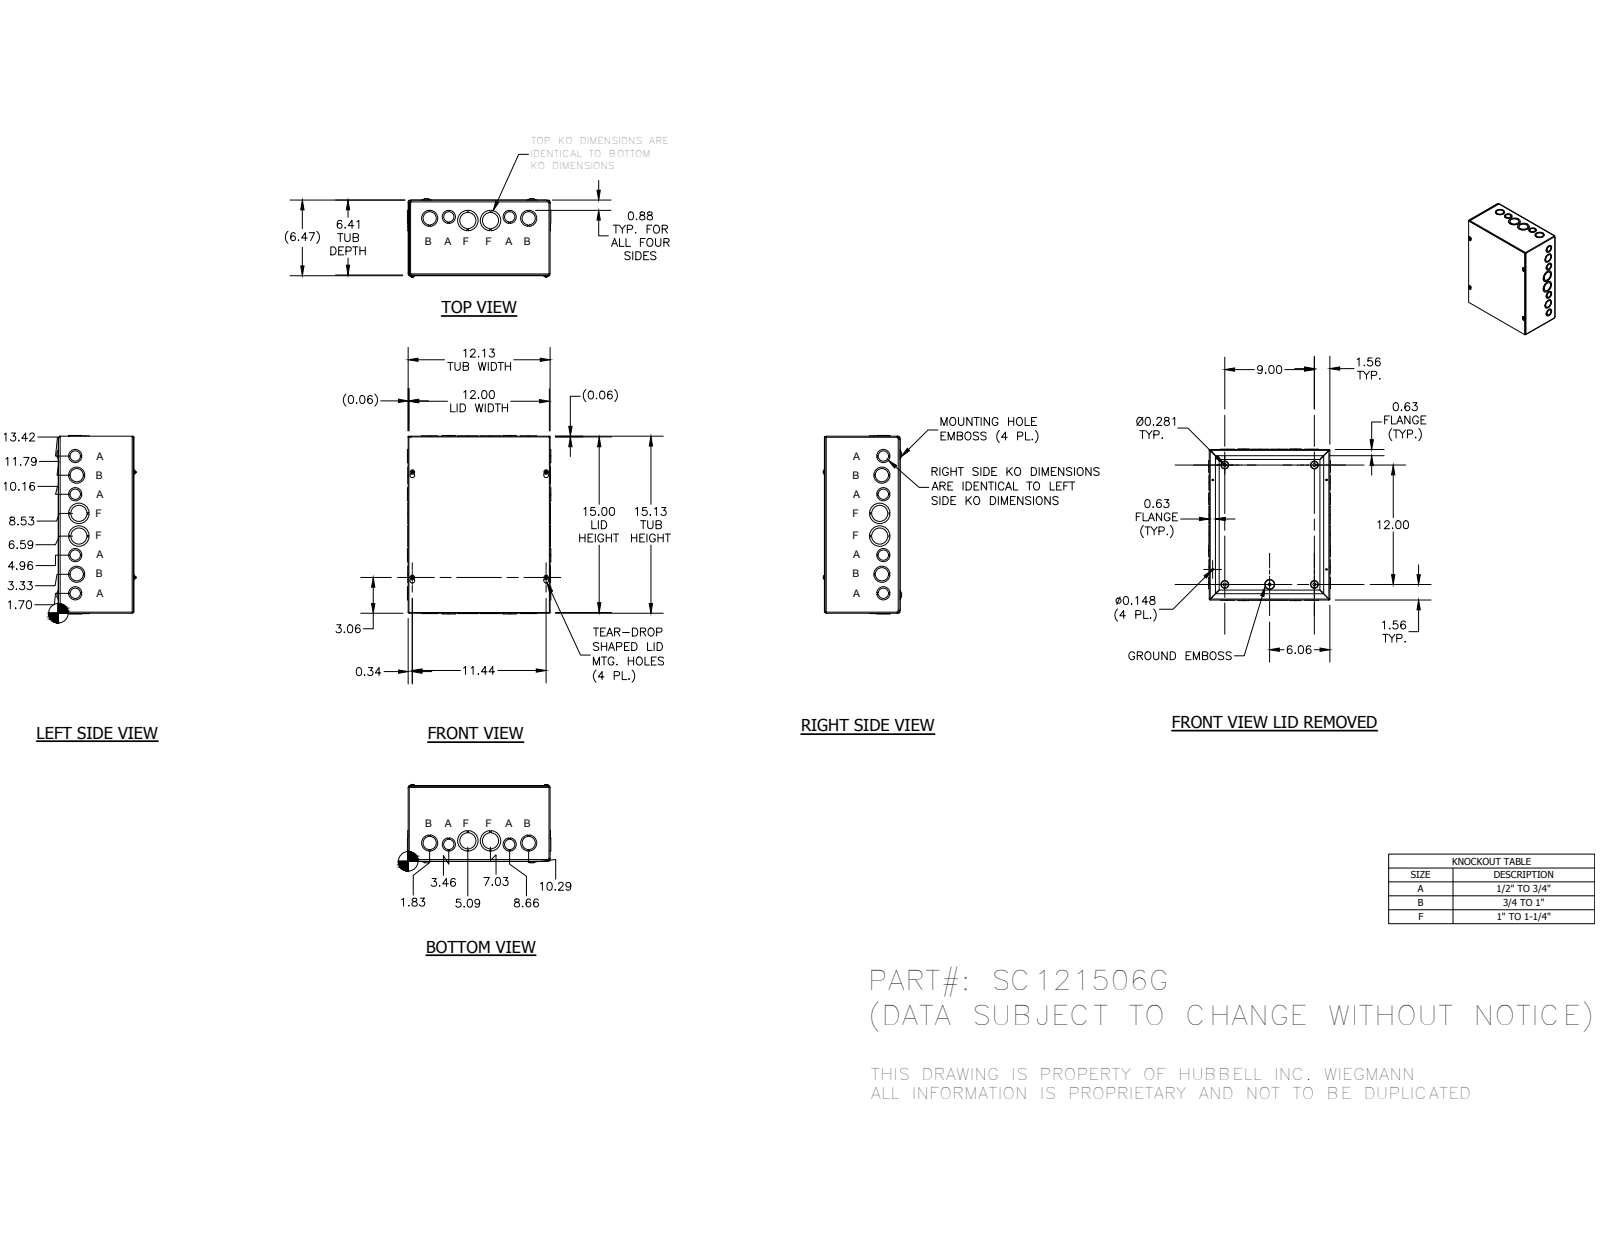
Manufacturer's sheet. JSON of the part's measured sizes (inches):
{"part_name": "SC1215GBKP; SC121506GWRA; SC1215GLID; 34056 (+1 more)", "step_written_by": "Autodesk Inventor 2014 (AUTOMOTIVE_DESIGN)", "units": "inches", "bodies": {"solids": 30, "faces": 1142, "planar": 750, "cylindrical": 241, "other": 151}, "overall_size": [15.249, 12.249, 6.693], "round_holes": [[1.125, 10], [1.375, 8], [0.875, 6], [0.148, 4], [0.3, 4], [1.75, 4], [0.165, 1]], "round_bosses_or_shafts": [[0.384, 4], [0.164, 4], [0.228, 1]], "partial_cylinders_radius": [[0.031, 8], [0.093, 8], [0.055, 4], [0.062, 4], [0.094, 4], [0.11, 4], [0.117, 4], [0.124, 4]], "face_to_face_distances": [0.062, 6.343, 6.405, 0.063, 6.406, 6.468, 15.063, 0.062, 12.125, 12.063], "hole_center_spacings": [1.635, 1.659, 1.933, 3.265, 3.584, 5.204, 6.831, 9]}
